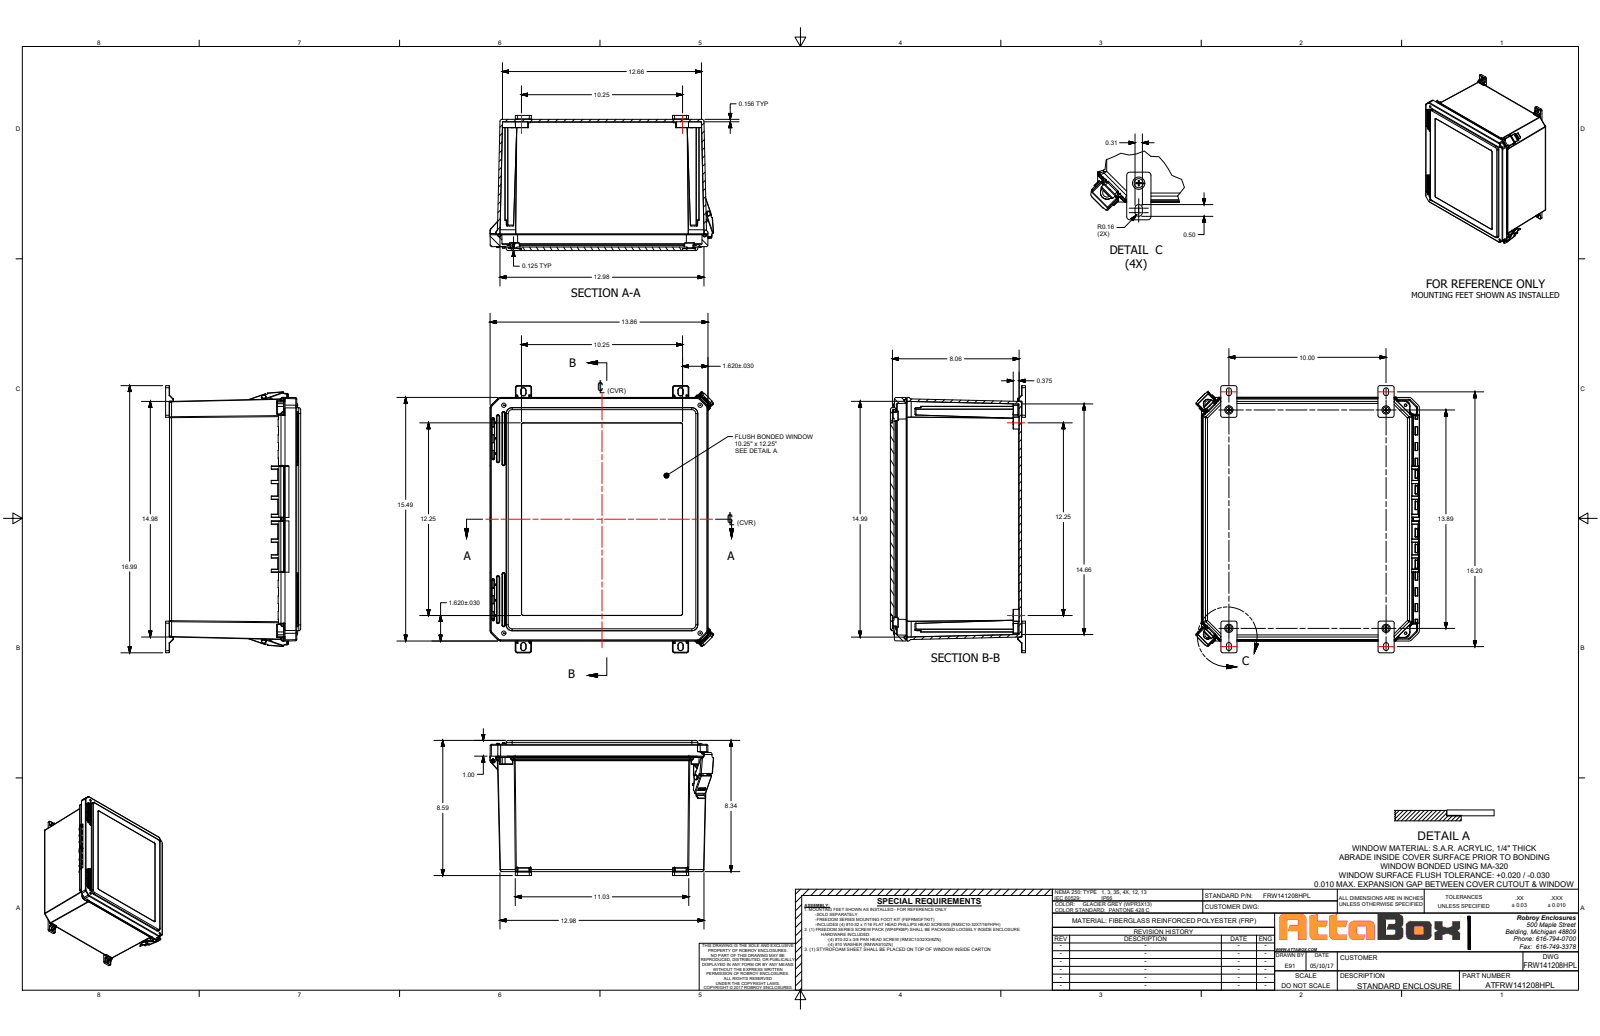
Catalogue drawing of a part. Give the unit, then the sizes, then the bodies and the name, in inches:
Units: inches
Overall size (bounding box): 16.2 × 14.216 × 8.767
Round holes (diameter × count): ⌀0.135 ×8, ⌀0.152 ×8, ⌀0.159 ×8, ⌀0.135 ×5, ⌀0.15 ×4, ⌀0.156 ×4, ⌀0.252 ×4, ⌀0.253 ×4, ⌀0.137 ×3, ⌀0.219 ×2, ⌀0.227 ×2, ⌀0.313 ×2
Round bosses / shafts (diameter × count): ⌀0.27 ×8, ⌀0.3 ×4, ⌀0.262 ×4, ⌀0.209 ×4, ⌀0.135 ×3, ⌀0.435 ×2, ⌀0.135 ×1
Partial cylindrical surfaces — rounded edges, fillets, slot ends (radius × count): R0.01 ×186, R0.005 ×110, R0.03 ×70, R0.02 ×54, R0.06 ×36, R0.09 ×26, R0.125 ×26, R0.03 ×24
Main face-to-face distances: 0.156, 0.16, 8.183, 8.339, 0.225, 7.958, 8.114, 0.158, 0.159, 0.125
Hole centre spacings: 14.243, 13.417, 13.836, 14.489, 14.49, 0.25, 12.489, 16.531
Volume: 158.8 in³ · Surface area: 1 889 in²
Bodies: 30 solids, 2514 faces (827 planar, 1072 cylindrical, 615 other)
Part name (STEP PRODUCT): FRW141208HPL
STEP written by: SolidWorks 2021 (AUTOMOTIVE_DESIGN)
